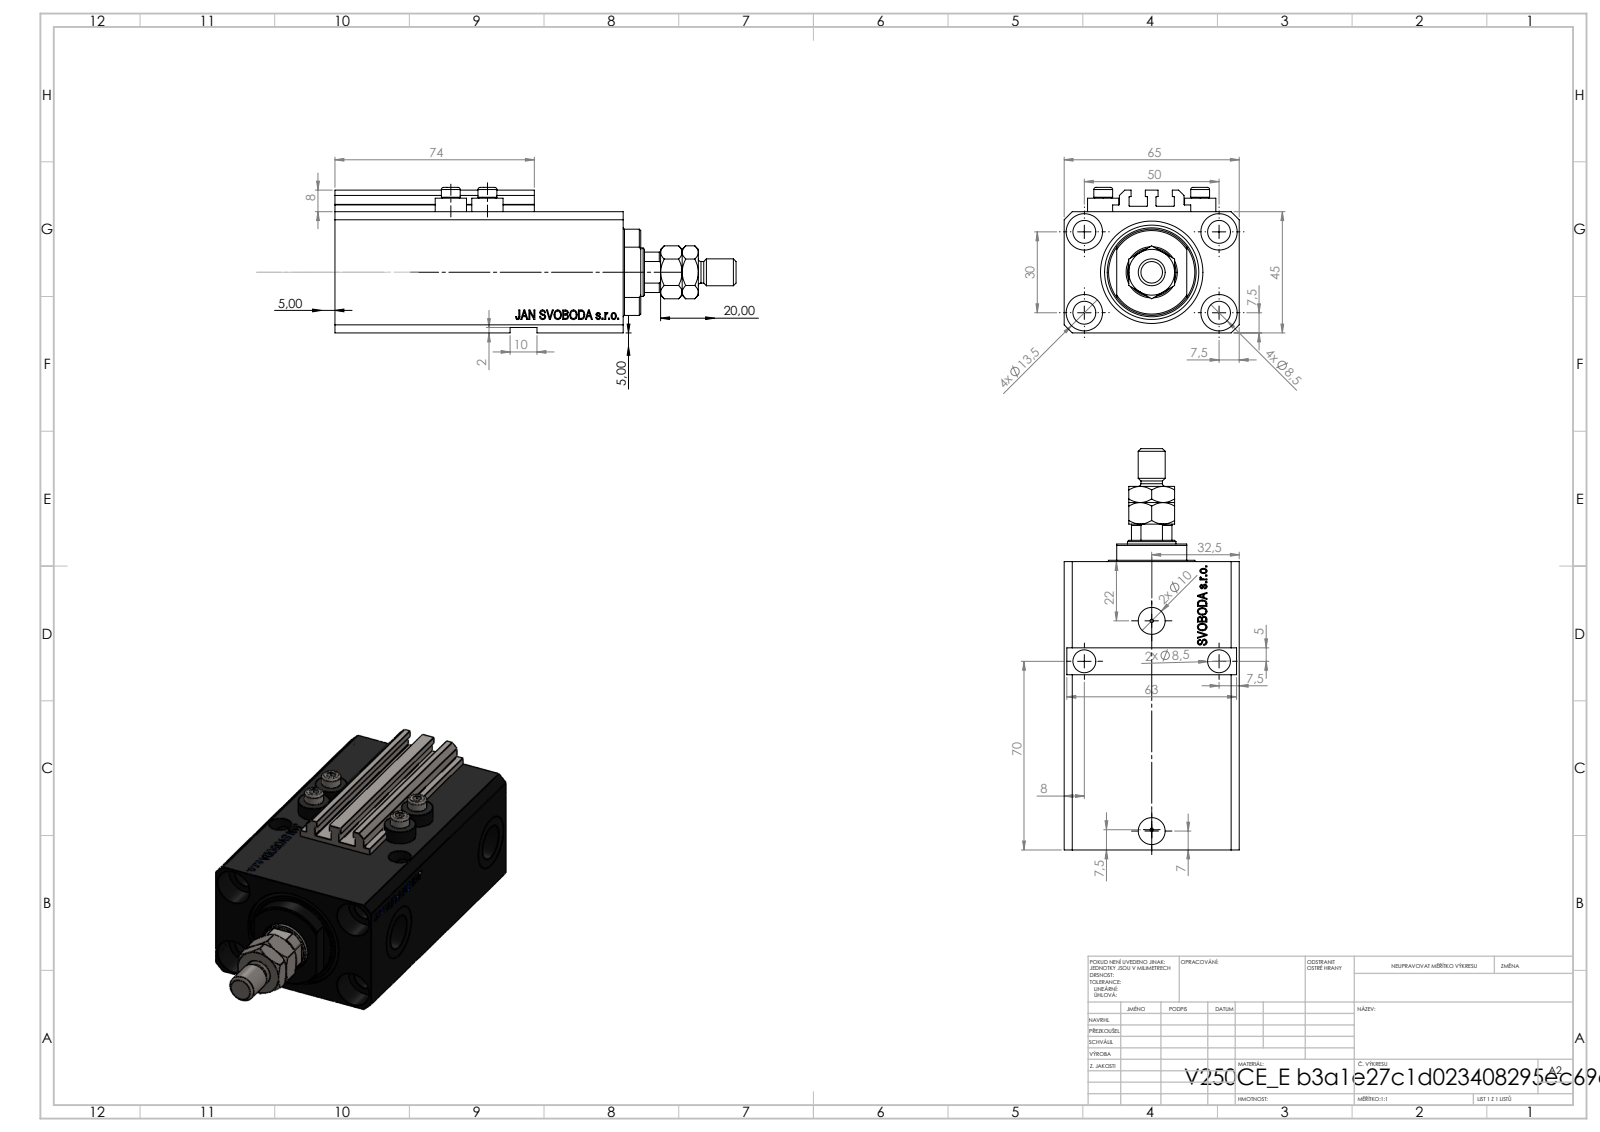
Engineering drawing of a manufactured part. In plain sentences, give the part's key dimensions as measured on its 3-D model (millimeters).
The part is named "ALLEN BOLT V250CE; V250CE_VC_E; V250CE_E_Body; MTA (+1 more)". Its 3-D file was written by "SolidWorks 2019 (CONFIG_CONTROL_DESIGN)". It is 9 solids with 1136 faces: 526 planar, 150 cylindrical and 460 other. Overall it measures 149 by 65 by 54 millimeters. Its volume is 277 886 cubic millimeters and its surface area 78 614 square millimeters. Round holes: 9 of diameter 8.5, 4 of diameter 1.25, 4 of diameter 4, 4 of diameter 13.5, 2 of diameter 10, 2 of diameter 13.16, 2 of diameter 20, 1 of diameter 18, 1 of diameter 25, 1 of diameter 38. Round bosses or shafts: 4 of diameter 11.6, 4 of diameter 7, 1 of diameter 10, 1 of diameter 8. Partial cylindrical surfaces (rounded edges, fillets, slot ends): 10 of radius 0.2, 1 of radius 8.5, 1 of radius 16. The main face-to-face distances are 45, 65, 14, 93, 2, 47, 107, 6.9, 20.5, 2.5. The hole center spacings are 29.15, 50, 13.6, 14.76, 15.12, 27.51, 27.89, 30.
